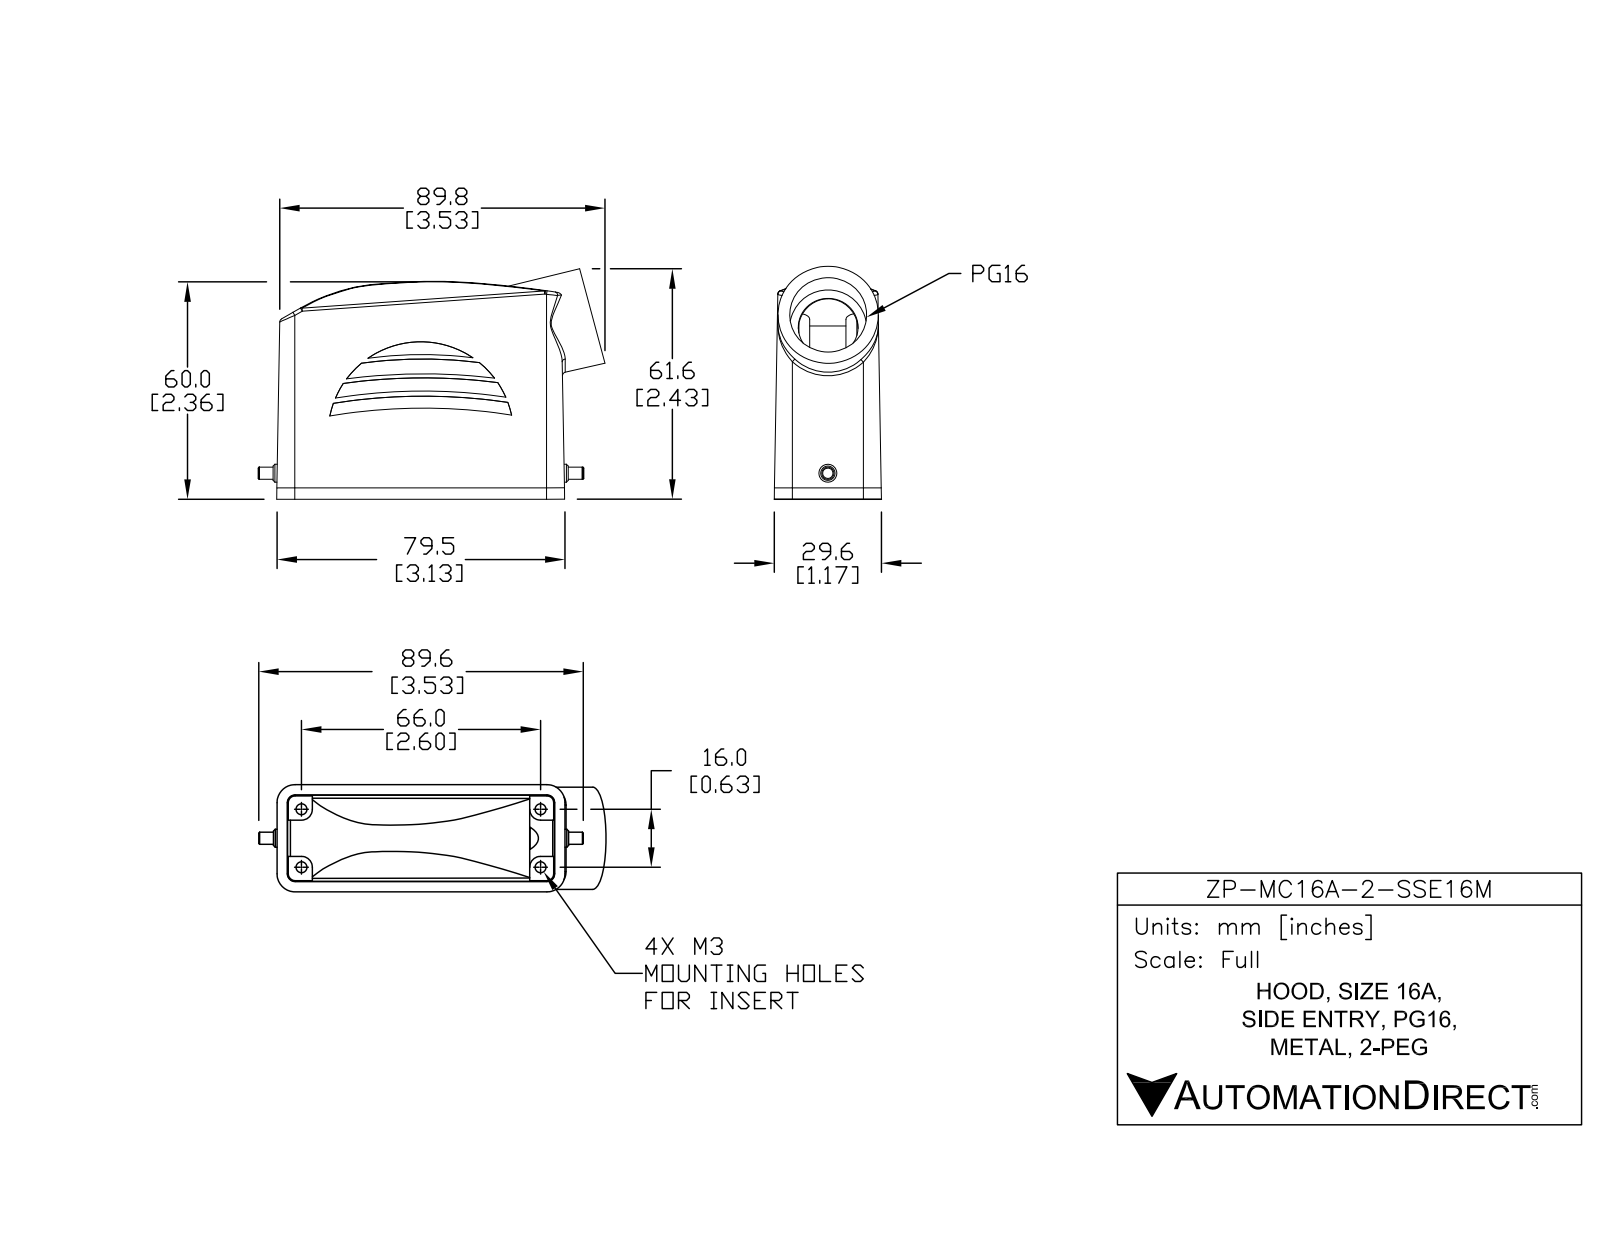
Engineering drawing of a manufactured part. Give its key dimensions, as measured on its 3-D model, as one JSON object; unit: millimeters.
{"part_name": "ZP-MC16A-2-SSE16M", "step_written_by": "SolidWorks 2014 (AUTOMOTIVE_DESIGN)", "units": "millimeters", "bodies": {"solids": 1, "faces": 166, "planar": 53, "cylindrical": 65, "other": 48}, "overall_size": [94.47, 61.68, 29.6], "volume_mm3": 42109, "surface_area_mm2": 27499, "round_holes": [[3, 4], [16.5, 1], [21.25, 1]], "round_bosses_or_shafts": [[27.75, 1], [4.95, 1], [3.35, 1]], "partial_cylinders_radius": [[3, 4], [1, 3], [25.65, 2], [112.15, 2], [125.15, 2], [154.36, 2], [155.71, 2], [159.01, 2]], "face_to_face_distances": [2.85, 2.62, 2.63, 60, 10, 13.3, 2.61, 14.6, 30.6, 16], "hole_center_spacings": [16, 66, 67.91]}
